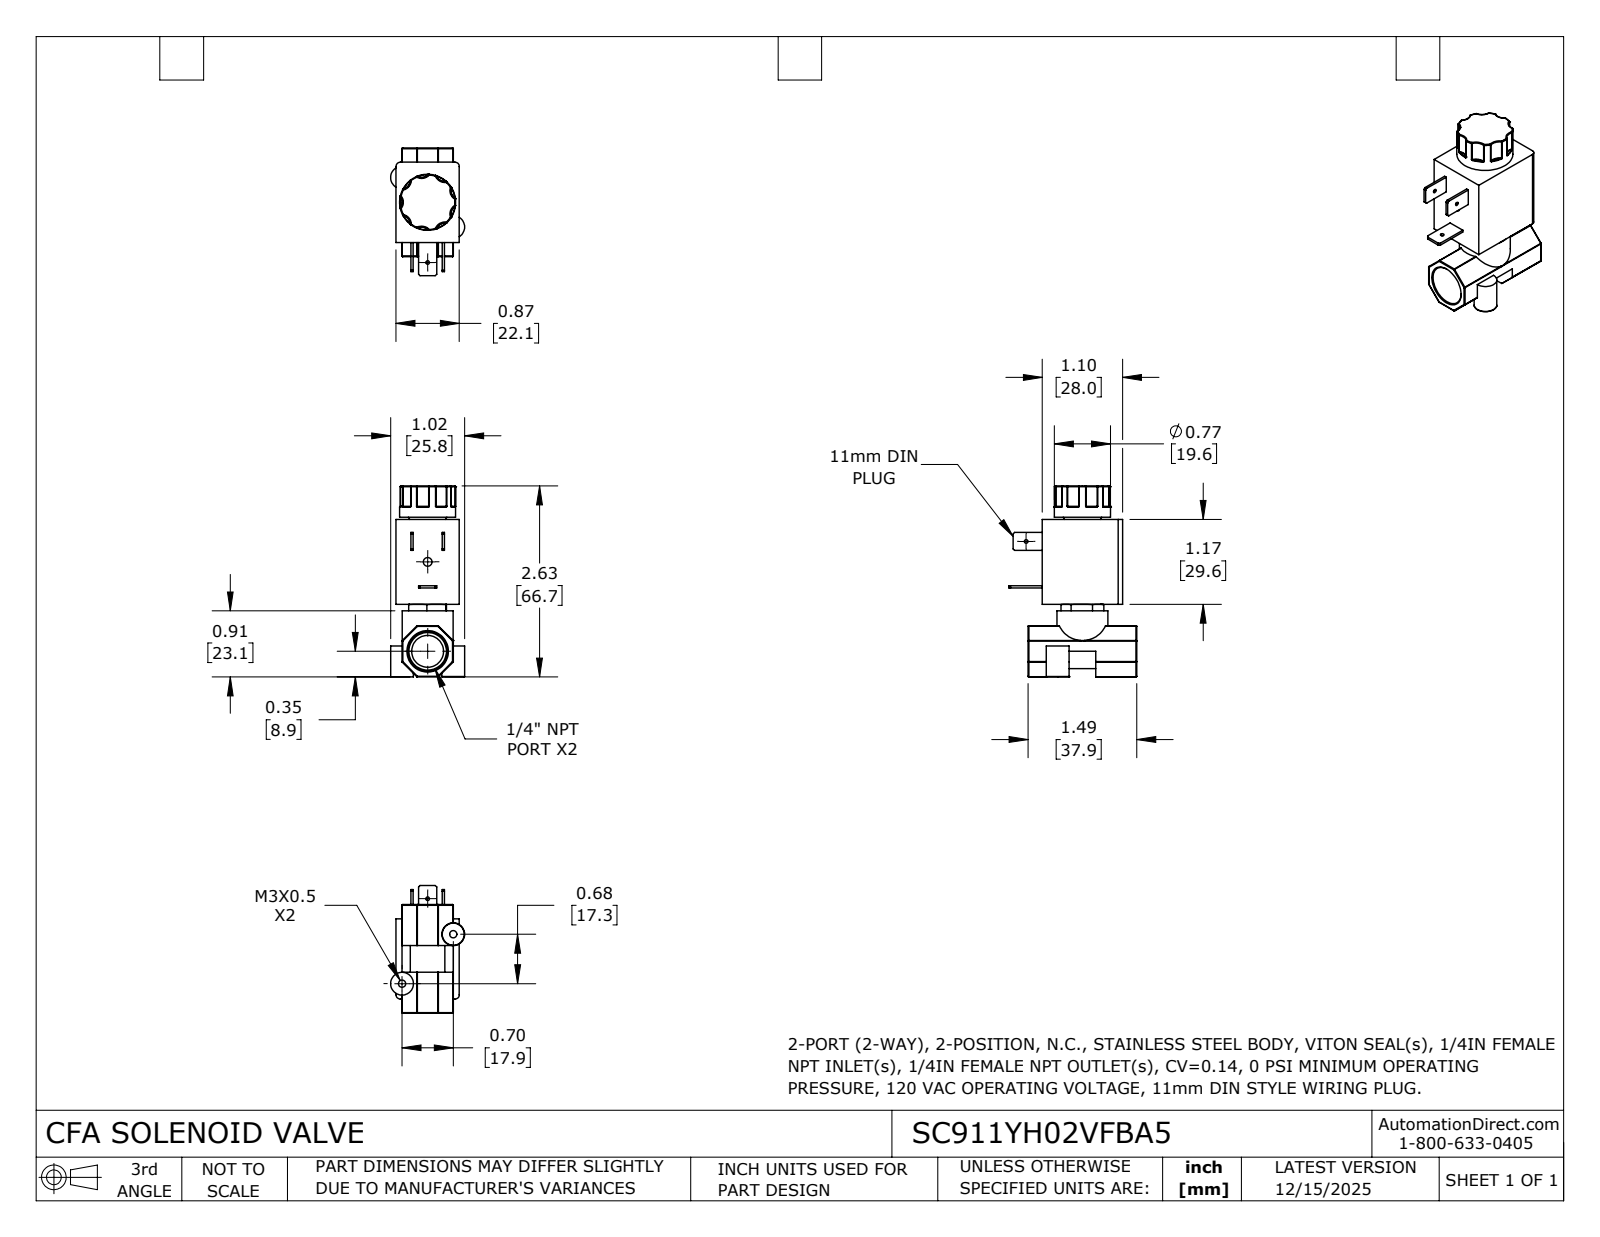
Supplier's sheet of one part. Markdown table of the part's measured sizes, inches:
| quantity | value |
| --- | --- |
| part name | SC911YH02VFBA5 |
| STEP written by | SolidWorks 2024 (CONFIG_CONTROL_DESIGN) |
| units | inches |
| bodies | 1 solid, 312 faces (74 planar, 89 cylindrical, 149 other) |
| overall size | 2.625 × 1.757 × 1.017 |
| volume | 1.799 in³ |
| surface area | 16.13 in² |
| round holes (diameter × count) | 0.05 × 2, 0.1 × 2, 0.12 × 1, 0.438 × 1 |
| round bosses / shafts (diameter × count) | 0.313 × 2, 0.77 × 1, 0.7 × 1 |
| partial cylindrical surfaces (radius × count) | 0.01 × 42, 0.133 × 7, 0.06 × 2, 0.132 × 2, 0.237 × 1 |
| main face-to-face distances | 0.87, 0.704, 1.104, 1.167, 0.083, 0.787, 0.46, 0.998, 2.165, 2.625 |
| hole center spacings | 0.602, 0.979, 1.22, 1.23 |
